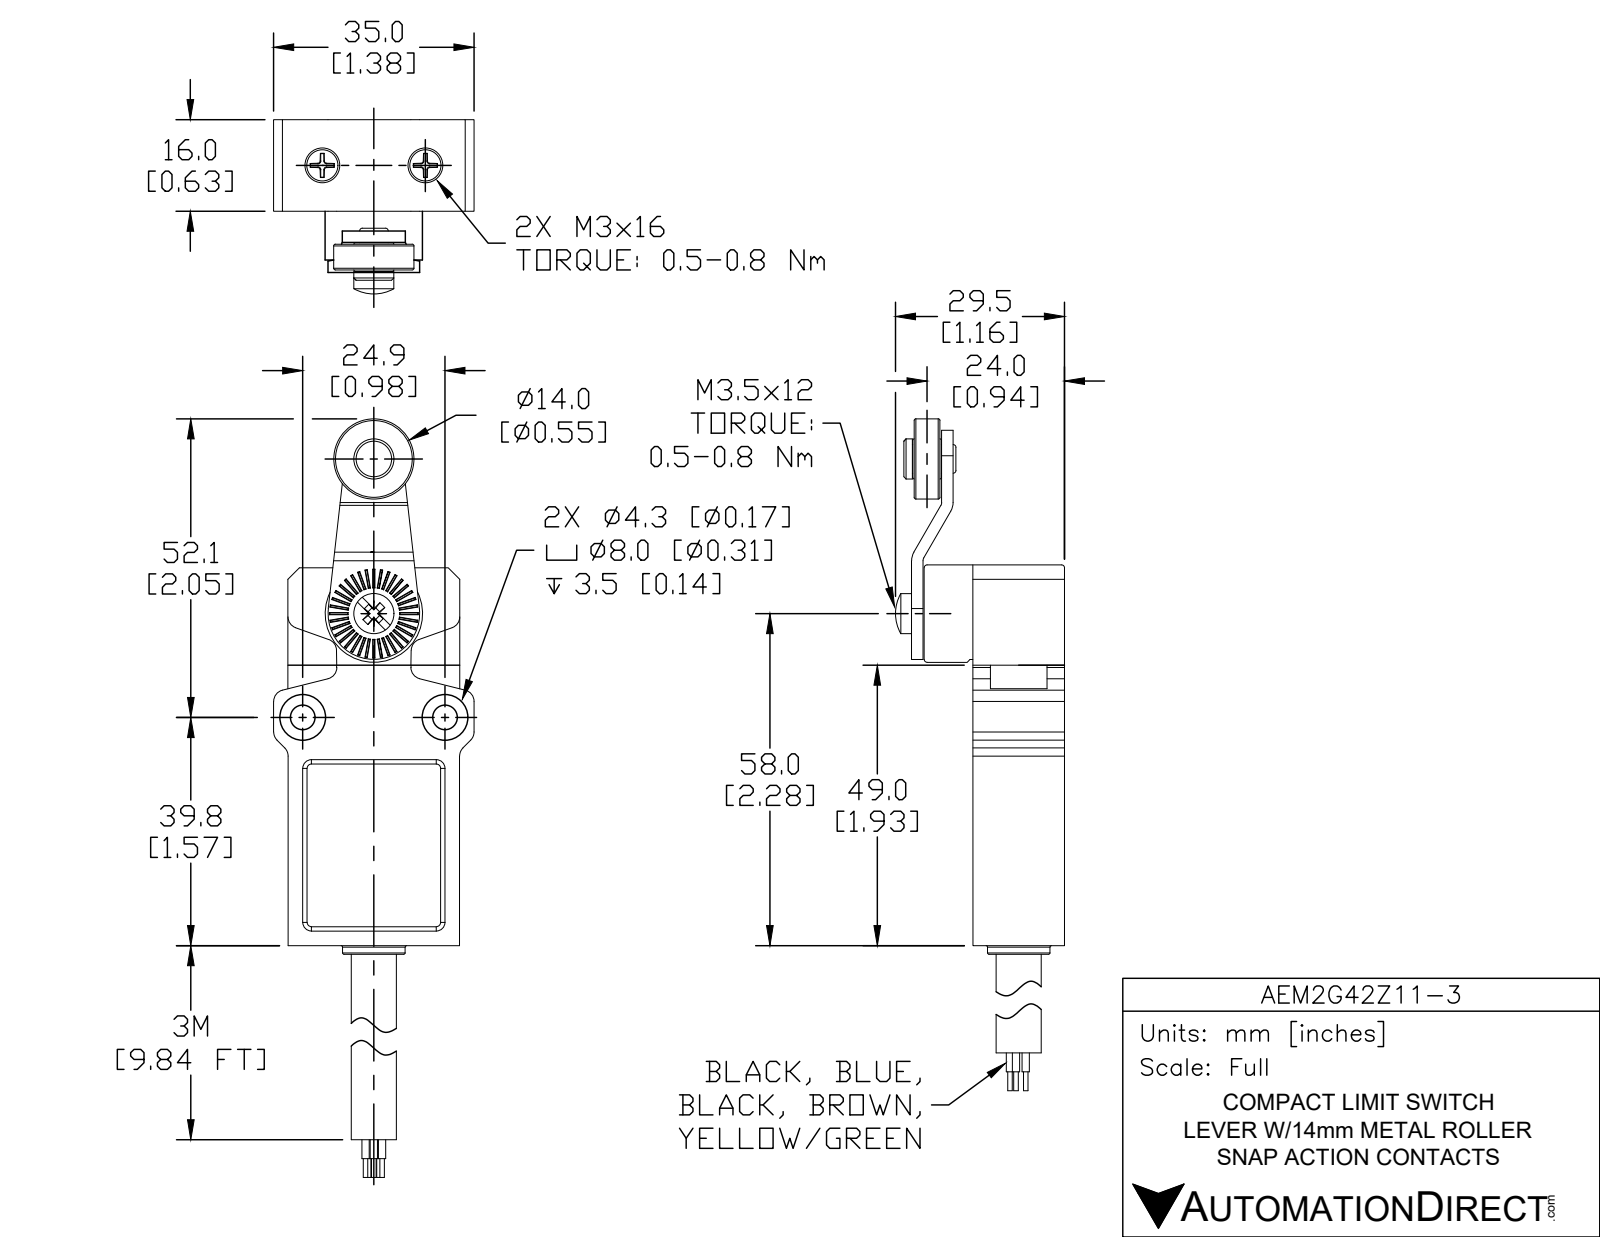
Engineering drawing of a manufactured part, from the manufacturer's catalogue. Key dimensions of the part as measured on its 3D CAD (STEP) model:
Part name (STEP PRODUCT): AEM2G42Z11-3_Default
STEP written by: SolidWorks 2021 (CONFIG_CONTROL_DESIGN)
Units: inches
Bodies: 4 solids, 309 faces (249 planar, 49 cylindrical, 11 other)
Overall size (bounding box): 4.124 × 1.378 × 1.184
Volume: 1.835 in³ · Surface area: 16.56 in²
Round holes (diameter × count): ⌀0.118 ×2, ⌀0.173 ×2, ⌀0.323 ×2, ⌀0.197 ×1
Round bosses / shafts (diameter × count): ⌀0.276 ×2, ⌀0.622 ×1, ⌀0.55 ×1, ⌀0.28 ×1, ⌀0.202 ×1, ⌀0.143 ×1
Partial cylindrical surfaces — rounded edges, fillets, slot ends (radius × count): R0.079 ×8, R0.06 ×2, R0.14 ×1, R0.192 ×1, R0.256 ×1, R0.313 ×1
Main face-to-face distances: 0.63, 1.181, 1.929, 0.354, 0.984, 0.28, 0.902, 0.08, 0.472, 0.434
Hole centre spacings: 0.863, 0.748, 0.984
